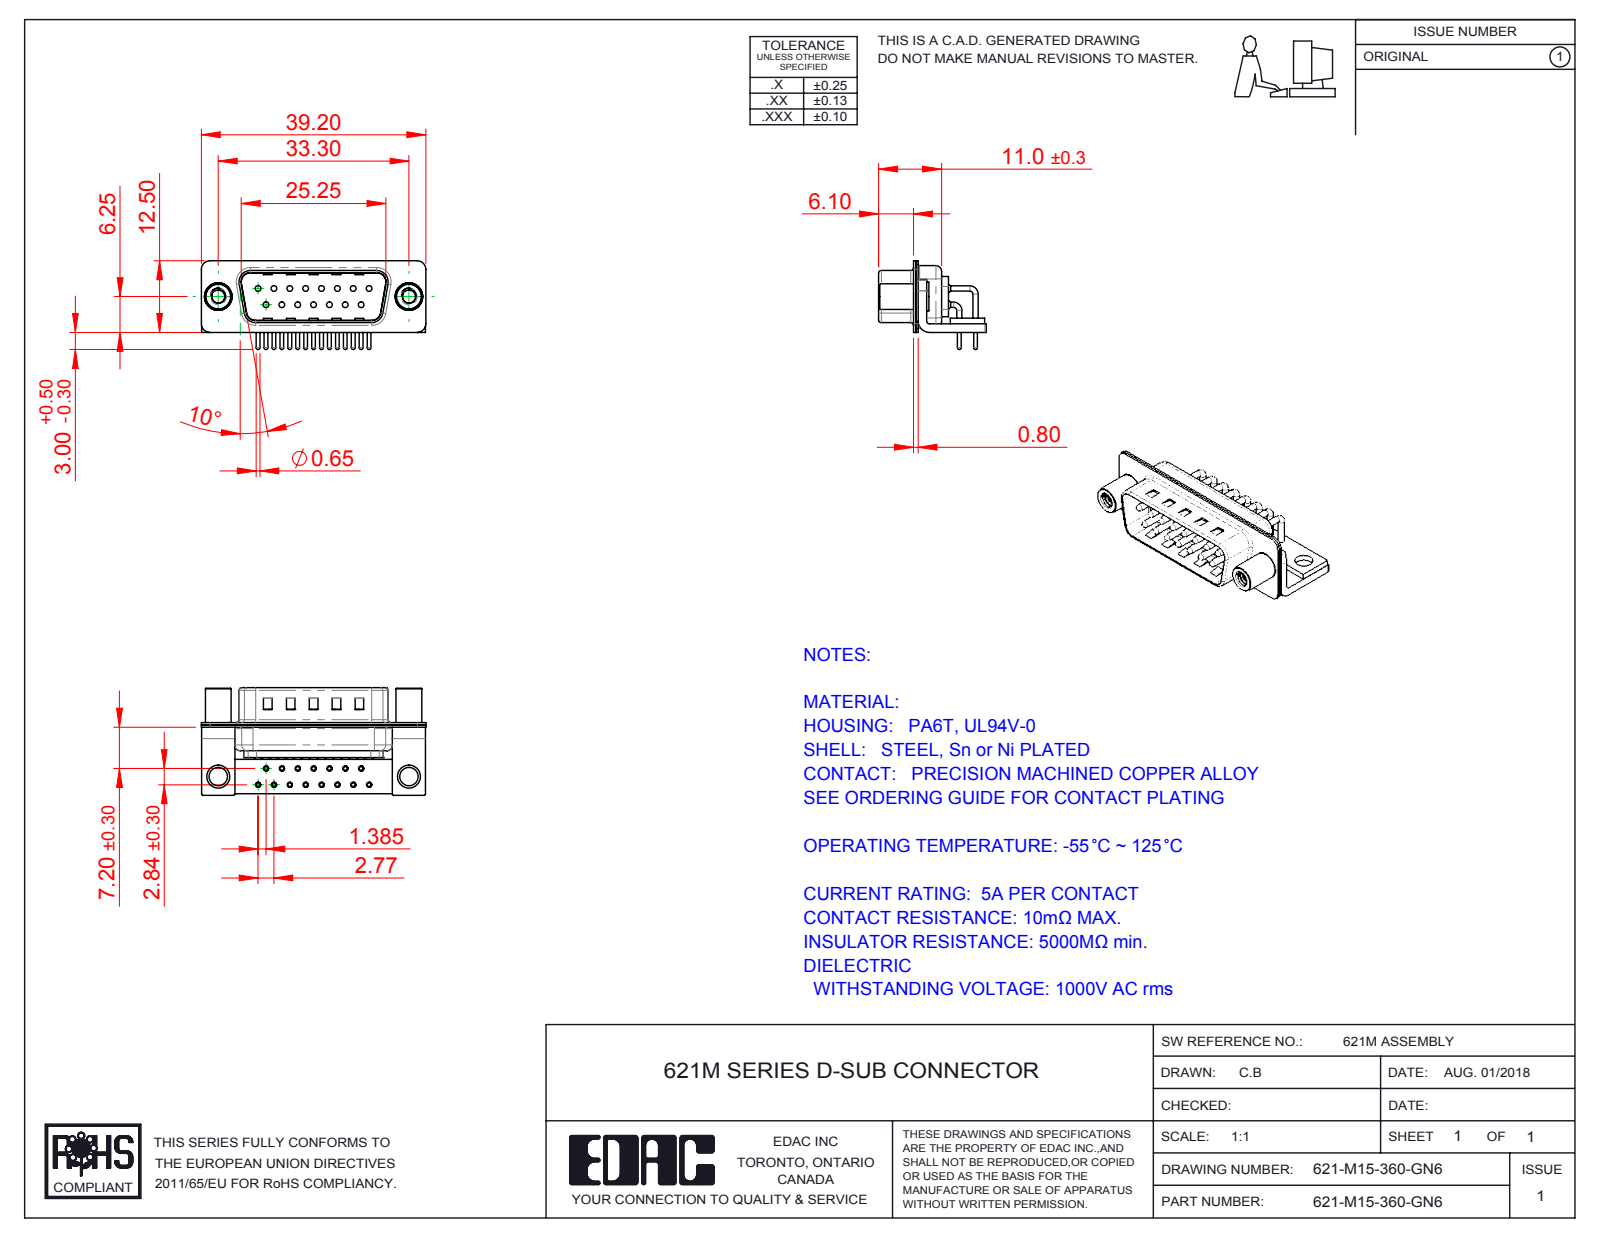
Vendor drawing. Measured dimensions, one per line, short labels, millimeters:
name: 621M Contact Row 1; 621-M15-360-GN6; 621M Stabilizer Bracket; 621M Shell Rear_15 Contacts (+5 more)
written by: SolidWorks 2016 (CONFIG_CONTROL_DESIGN)
unit: mm
bodies: 23 solids, 2120 faces (1127 planar, 767 cylindrical, 226 other)
size: 39.2 × 18.8 × 15.49
volume: 2 498 mm³; area: 6 670 mm²
holes: 15× ⌀0.9, 15× ⌀1, 15× ⌀1.7, 15× ⌀2, 2× ⌀2.26, 2× ⌀3.2, 2× ⌀4, 2× ⌀4.8
bosses: 22× ⌀0.9, 15× ⌀1.5, 15× ⌀0.65, 2× ⌀5, 2× ⌀4.9, 2× ⌀4.5
rounds: 16× R0.25, 16× R1.5, 15× R1.01, 13× R2, 9× R0.5, 8× R1.6, 4× R0.6, 4× R0.65
face distances: 0.4, 0.85, 1.5, 0.8, 1.25, 10.4, 9.55, 1.9, 1, 8.3
hole spacings: 3.16, 2.77, 5.54, 8.31, 11.08, 5.03, 5.04, 7.48
